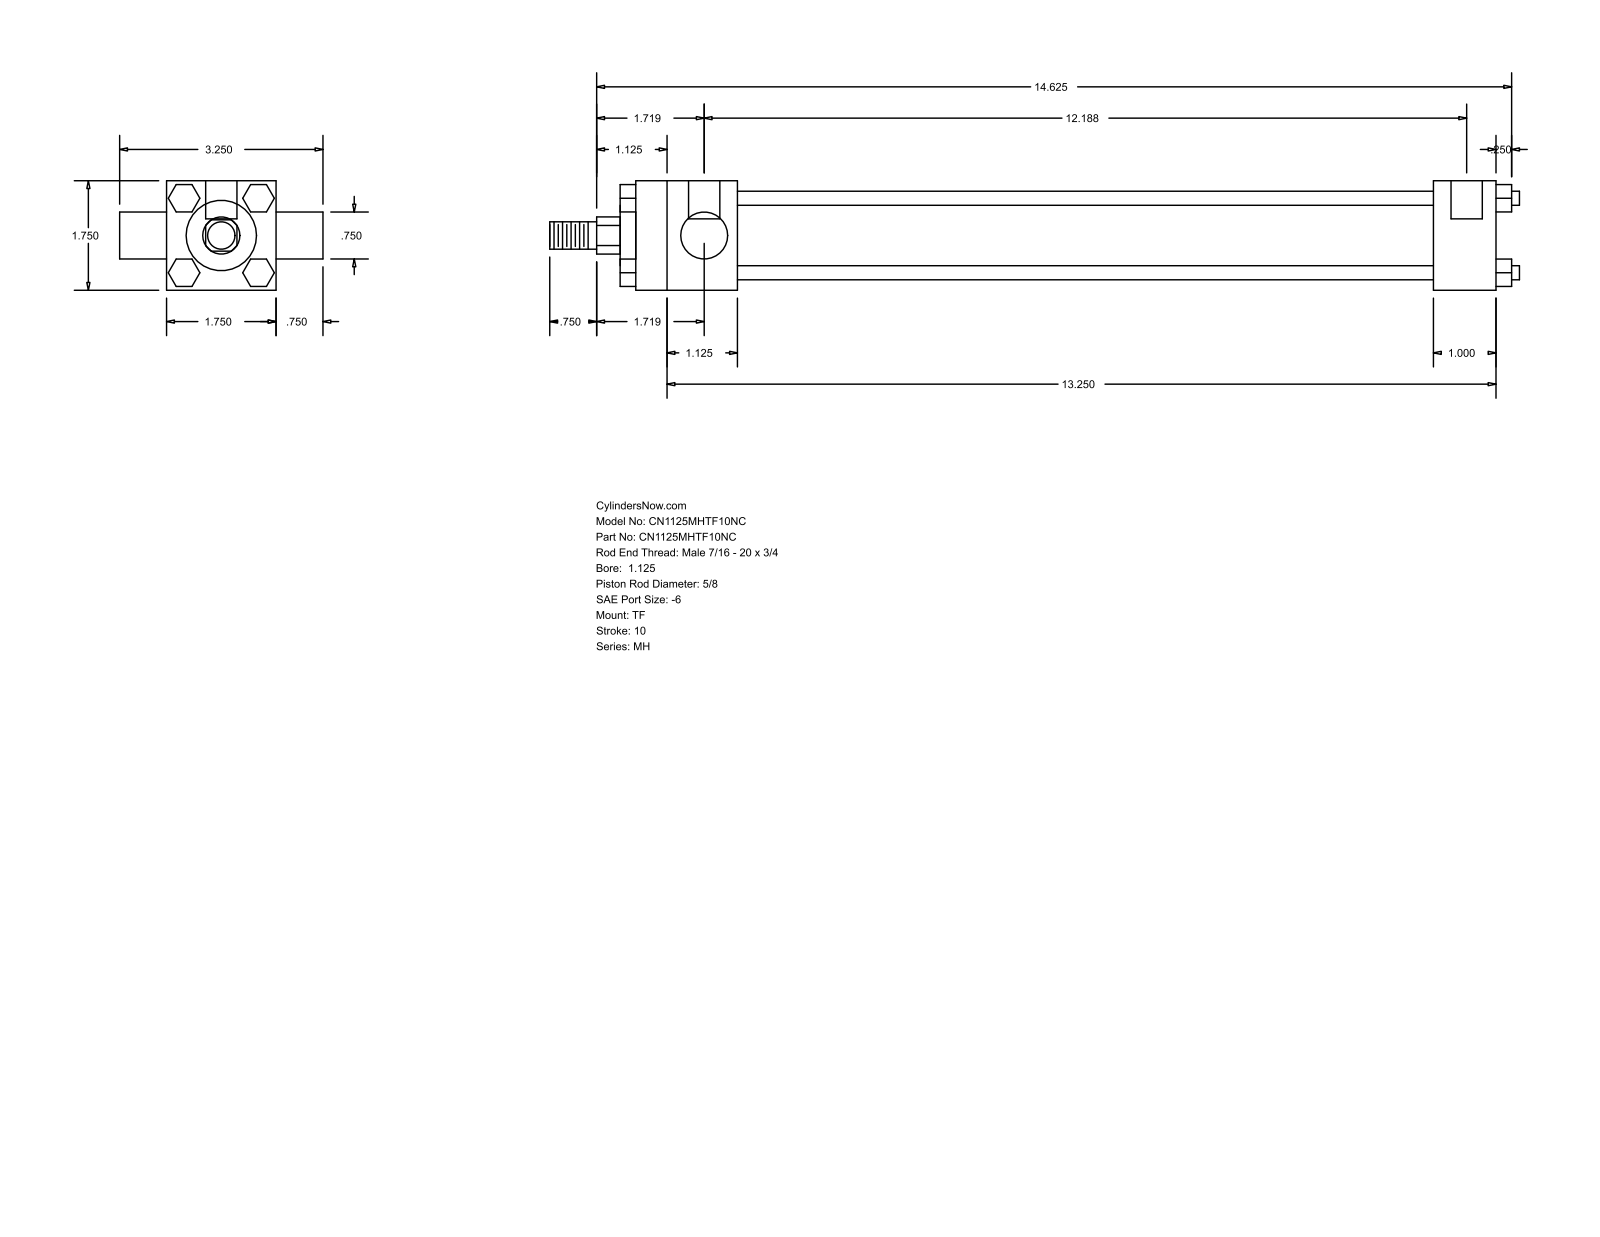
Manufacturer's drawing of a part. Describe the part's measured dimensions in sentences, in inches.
The part is named "MH_TF__0112_0.625". Its 3-D file was written by "GSSL Pune (CONFIG_CONTROL_DESIGN)". It is 0 solids with 120 faces: 92 planar, 28 cylindrical and 0 other. Overall it measures 15.5 by 3.25 by 1.75 inches. Round holes: 3 of diameter 0.219, 2 of diameter 0.5. Round bosses or shafts: 4 of diameter 0.225, 1 of diameter 1.375, 1 of diameter 1.125, 1 of diameter 0.75, 1 of diameter 0.625, 1 of diameter 0.437. Partial cylindrical surfaces (rounded edges, fillets, slot ends): 1 of radius 0.297. The main face-to-face distances are 1.75, 0.437, 11.125, 12.125, 1, 1.625, 12.75, 13.75, 1.875, 0.25. The hole center spacings are 0.125, 12.063, 12.187.
